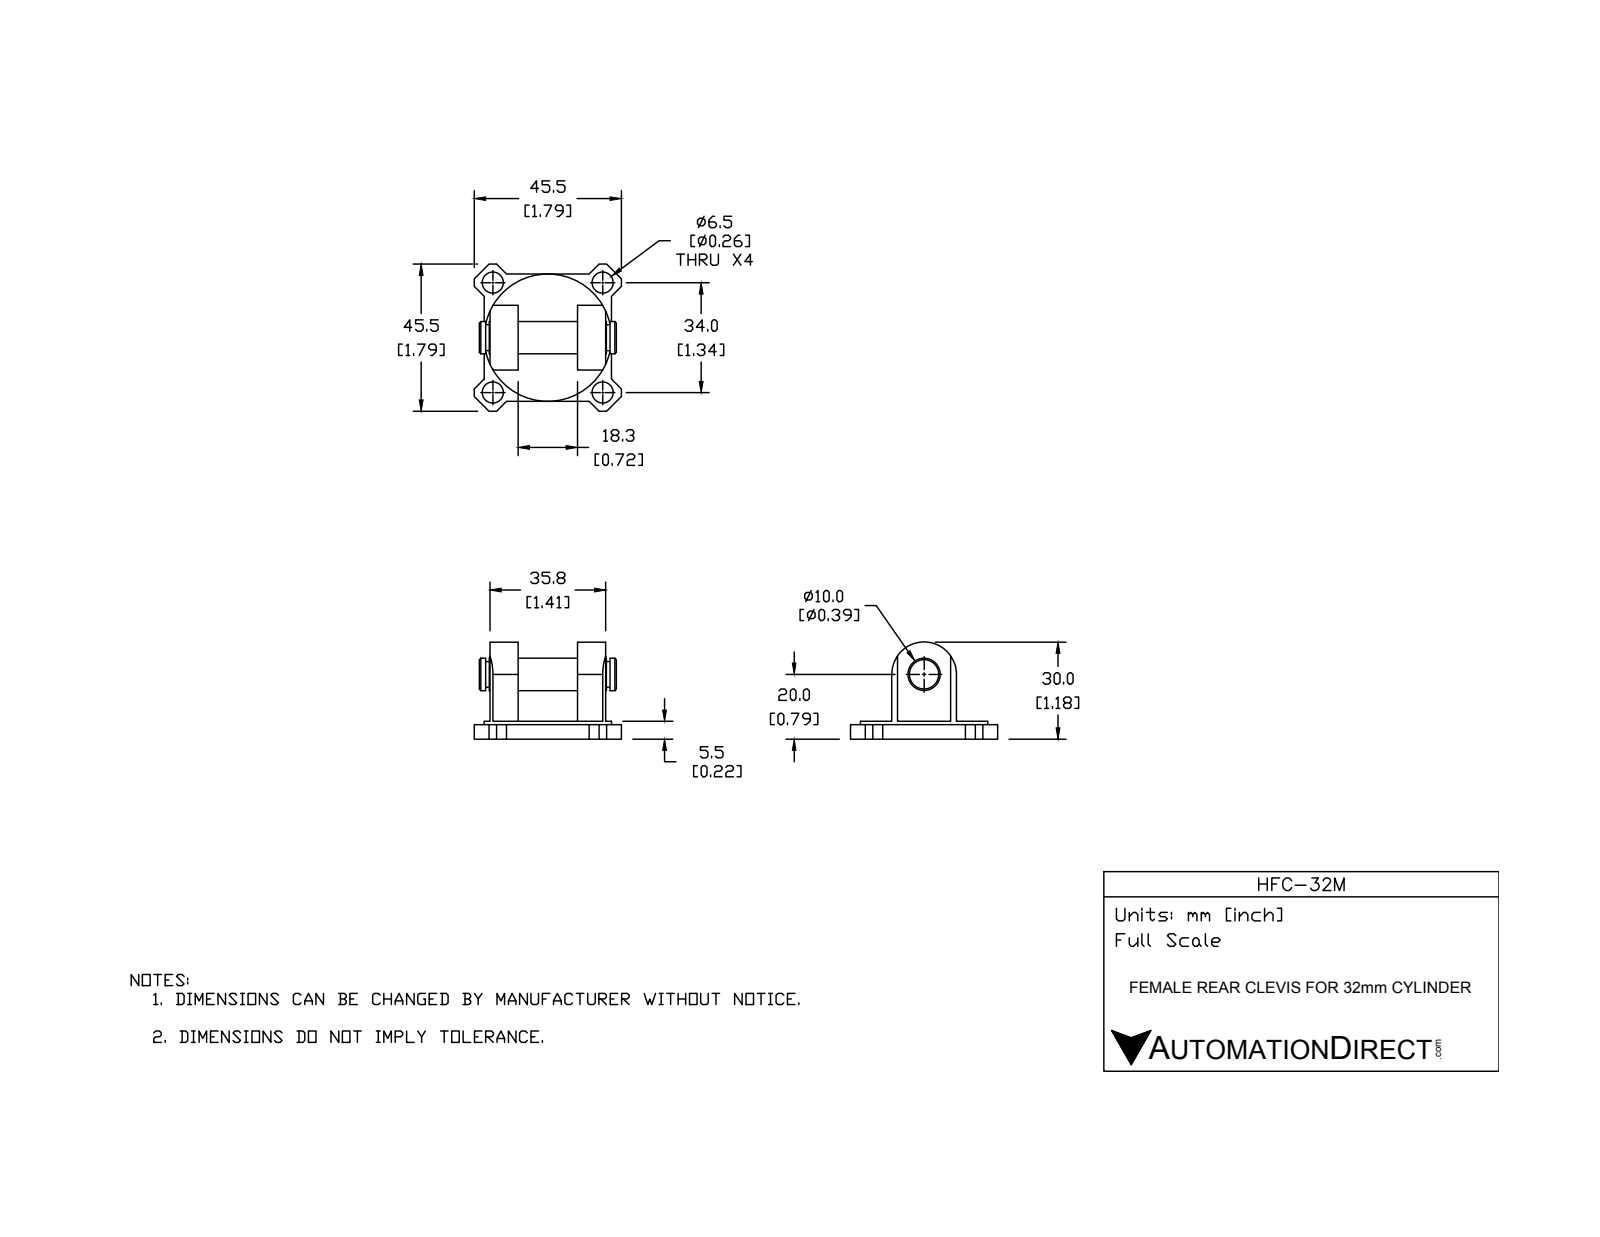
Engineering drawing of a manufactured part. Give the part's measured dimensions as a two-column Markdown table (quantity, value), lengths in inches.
| quantity | value |
| --- | --- |
| part name | HFC-32M |
| STEP written by | SolidWorks 2015 (CONFIG_CONTROL_DESIGN) |
| units | inches |
| bodies | 2 solids, 76 faces (46 planar, 26 cylindrical, 4 other) |
| overall size | 1.791 × 1.791 × 1.181 |
| volume | 1.088 in³ |
| surface area | 13.41 in² |
| round holes (diameter × count) | 0.256 × 4 |
| round bosses / shafts (diameter × count) | 1.55 × 1, 0.394 × 1, 0.315 × 1 |
| partial cylindrical surfaces (radius × count) | 0.394 × 1 |
| main face-to-face distances | 0.217, 0.344, 1.065, 0.72, 0.177, 0.039, 1.409, 0.07, 0.415, 1.135 |
| hole center spacings | 1.339, 1.893 |
